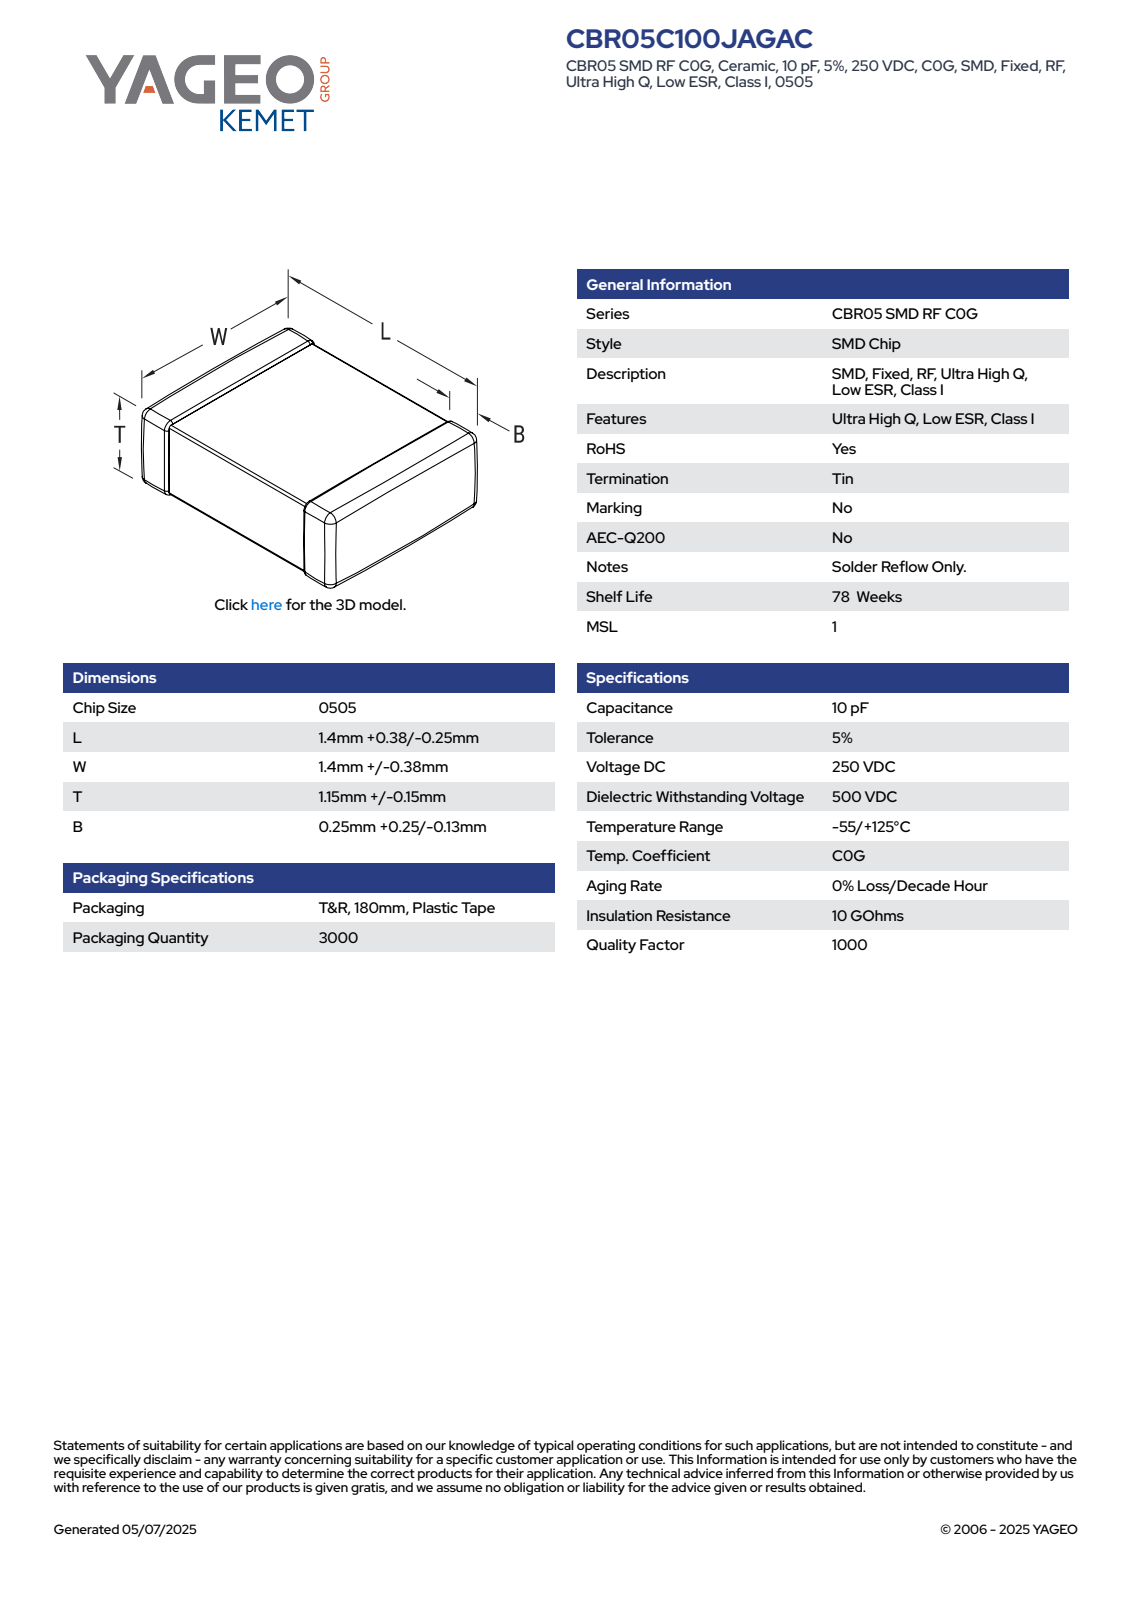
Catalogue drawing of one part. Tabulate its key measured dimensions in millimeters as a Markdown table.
| quantity | value |
| --- | --- |
| part name | CCS_CCSTDNOS_0505_L1.78W1.78T1.3B0.5 |
| STEP written by | SolidWorks 2014 (AUTOMOTIVE_DESIGN) |
| units | millimeters |
| bodies | 4 solids, 125 faces (71 planar, 38 cylindrical, 16 other) |
| overall size | 1.78 × 1.78 × 1.3 |
| volume | 4 mm³ |
| surface area | 15 mm² |
| main face-to-face distances | 1.78, 1.26, 1.74, 1.3, 1.22, 1.7, 1.27, 1.23, 0.89, 0.85 |
